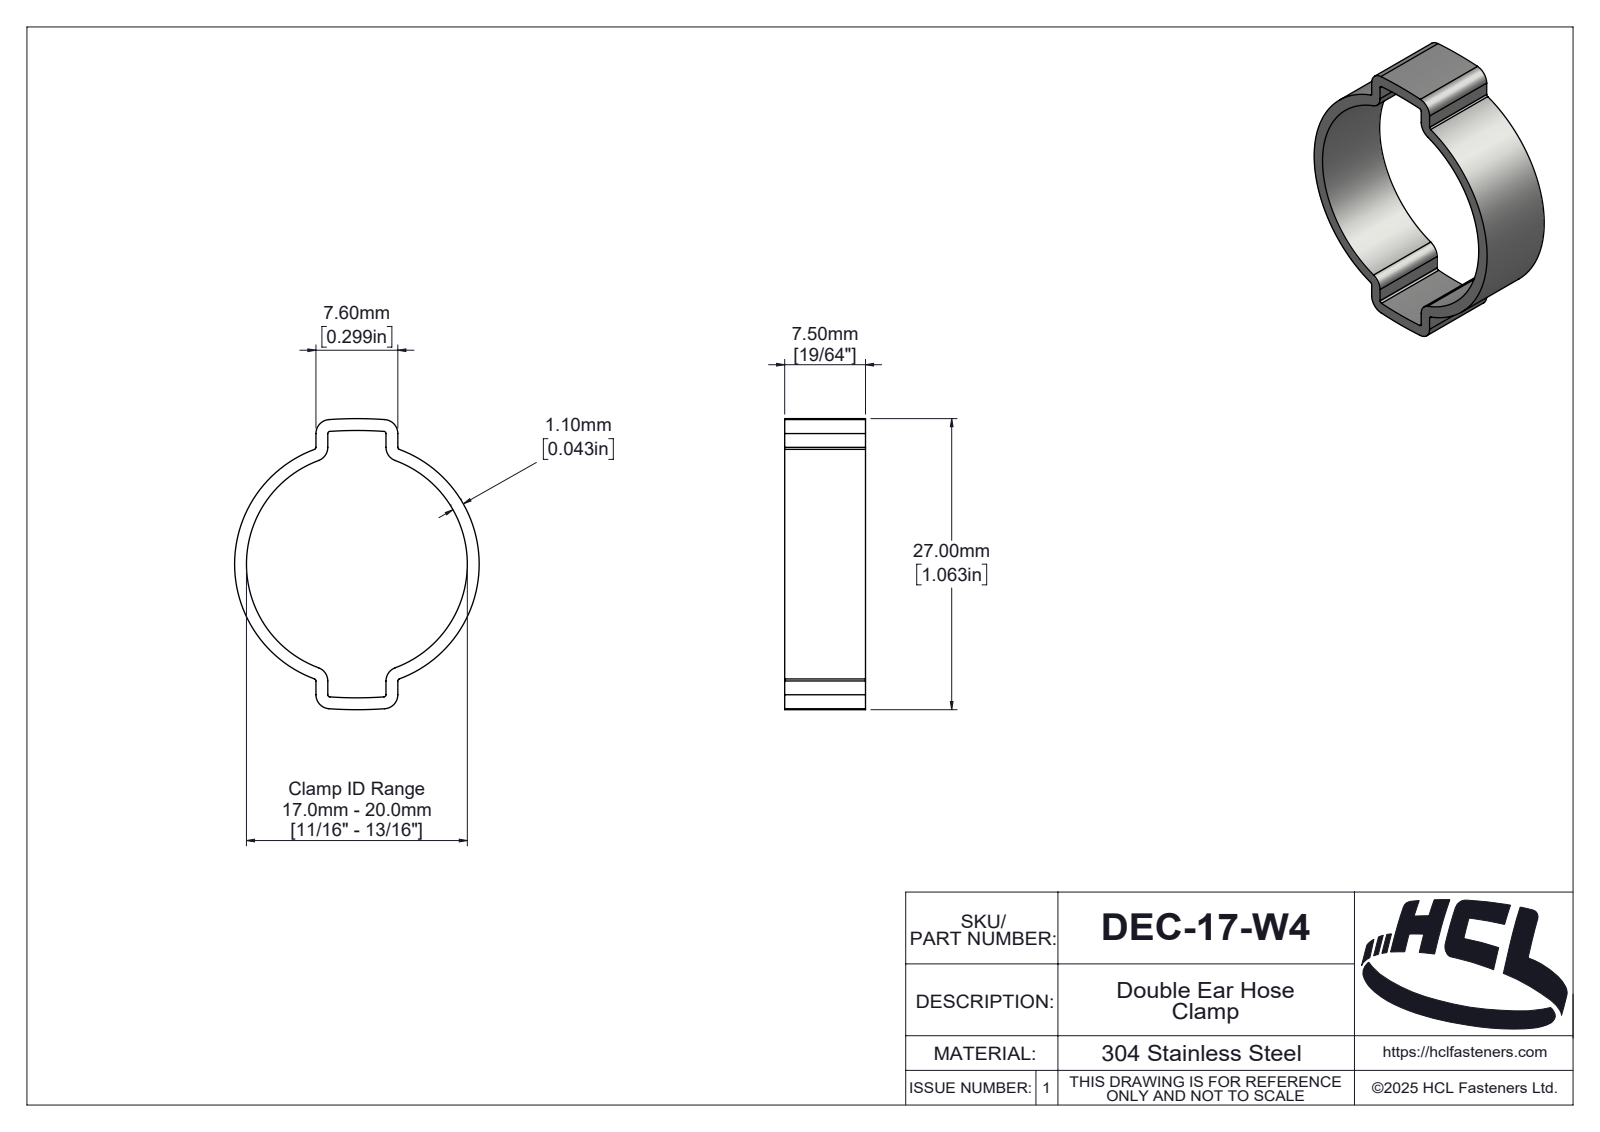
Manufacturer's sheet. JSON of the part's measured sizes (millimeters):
{"part_name": "DEC-17-W4", "step_written_by": "SolidWorks 2025 (AUTOMOTIVE_DESIGN)", "units": "millimeters", "bodies": {"solids": 1, "faces": 137, "planar": 12, "cylindrical": 67, "other": 58}, "overall_size": [27, 22.7, 7.5], "volume_mm3": 627, "surface_area_mm2": 1312, "partial_cylinders_radius": [[0.2, 8], [1.3, 8], [36.5, 2], [37.6, 2], [0.2, 1], [0.81, 1], [1.01, 1], [1.06, 1]], "face_to_face_distances": [7.5, 1.1, 6.5, 7.6, 5.4, 3.68, 2.58, 2.82, 3.92, 3.53]}
